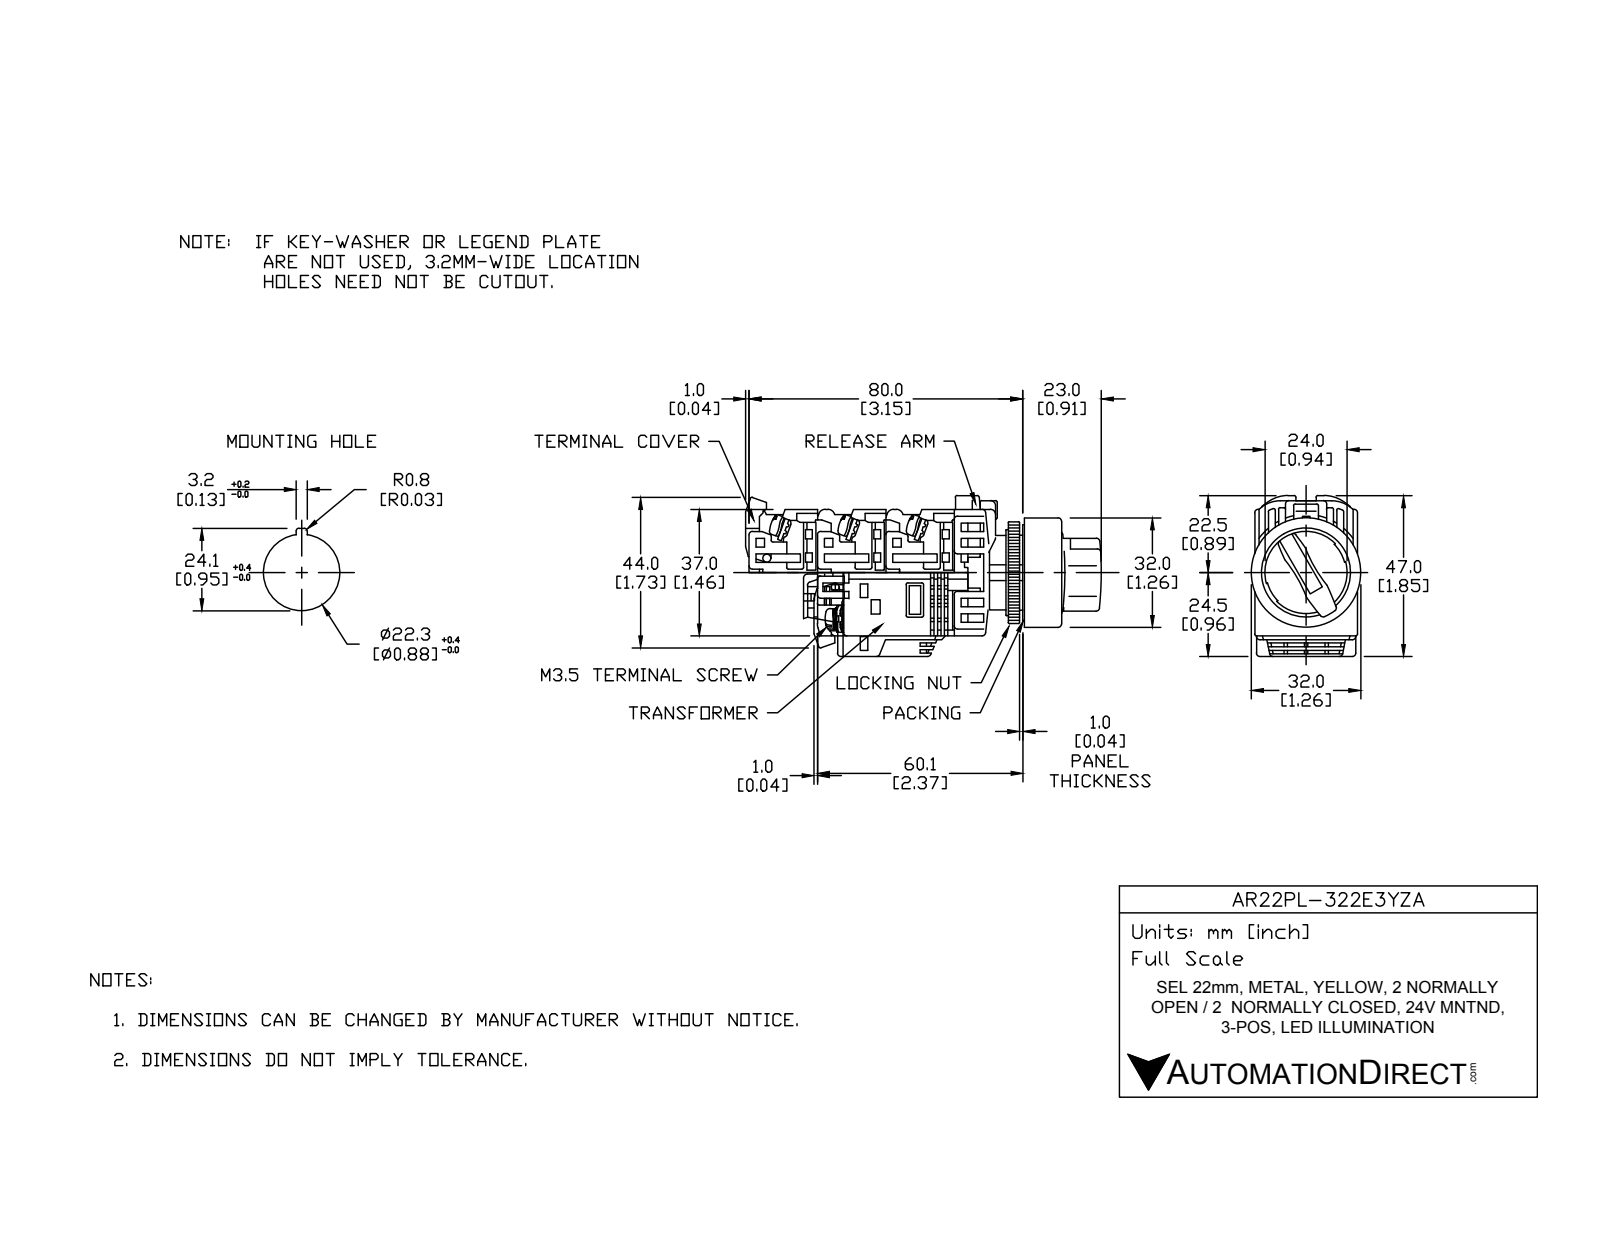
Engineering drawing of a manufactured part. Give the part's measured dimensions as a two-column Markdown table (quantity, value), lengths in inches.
| quantity | value |
| --- | --- |
| part name | AR22PL-322E3YZA |
| STEP written by | SolidWorks 2017 (AUTOMOTIVE_DESIGN) |
| units | inches |
| bodies | 33 solids, 744 faces (524 planar, 181 cylindrical, 39 other) |
| overall size | 4.114 × 1.725 × 1.26 |
| volume | 3.913 in³ |
| surface area | 54.8 in² |
| round holes (diameter × count) | 0.858 × 1, 0.866 × 1, 0.984 × 1, 1.22 × 1 |
| round bosses / shafts (diameter × count) | 0.197 × 10, 1.26 × 1, 1.201 × 1, 1.173 × 1, 0.945 × 1, 0.856 × 1, 0.669 × 1 |
| partial cylindrical surfaces (radius × count) | 0.02 × 66, 0.069 × 8, 0.039 × 6, 0.197 × 4, 0.157 × 2, 0.472 × 1, 0.653 × 1, 0.693 × 1 |
| main face-to-face distances | 0.787, 0.039, 0.709, 1.575, 1.142, 0.118, 0.354, 0.394, 0.079, 0.748 |
